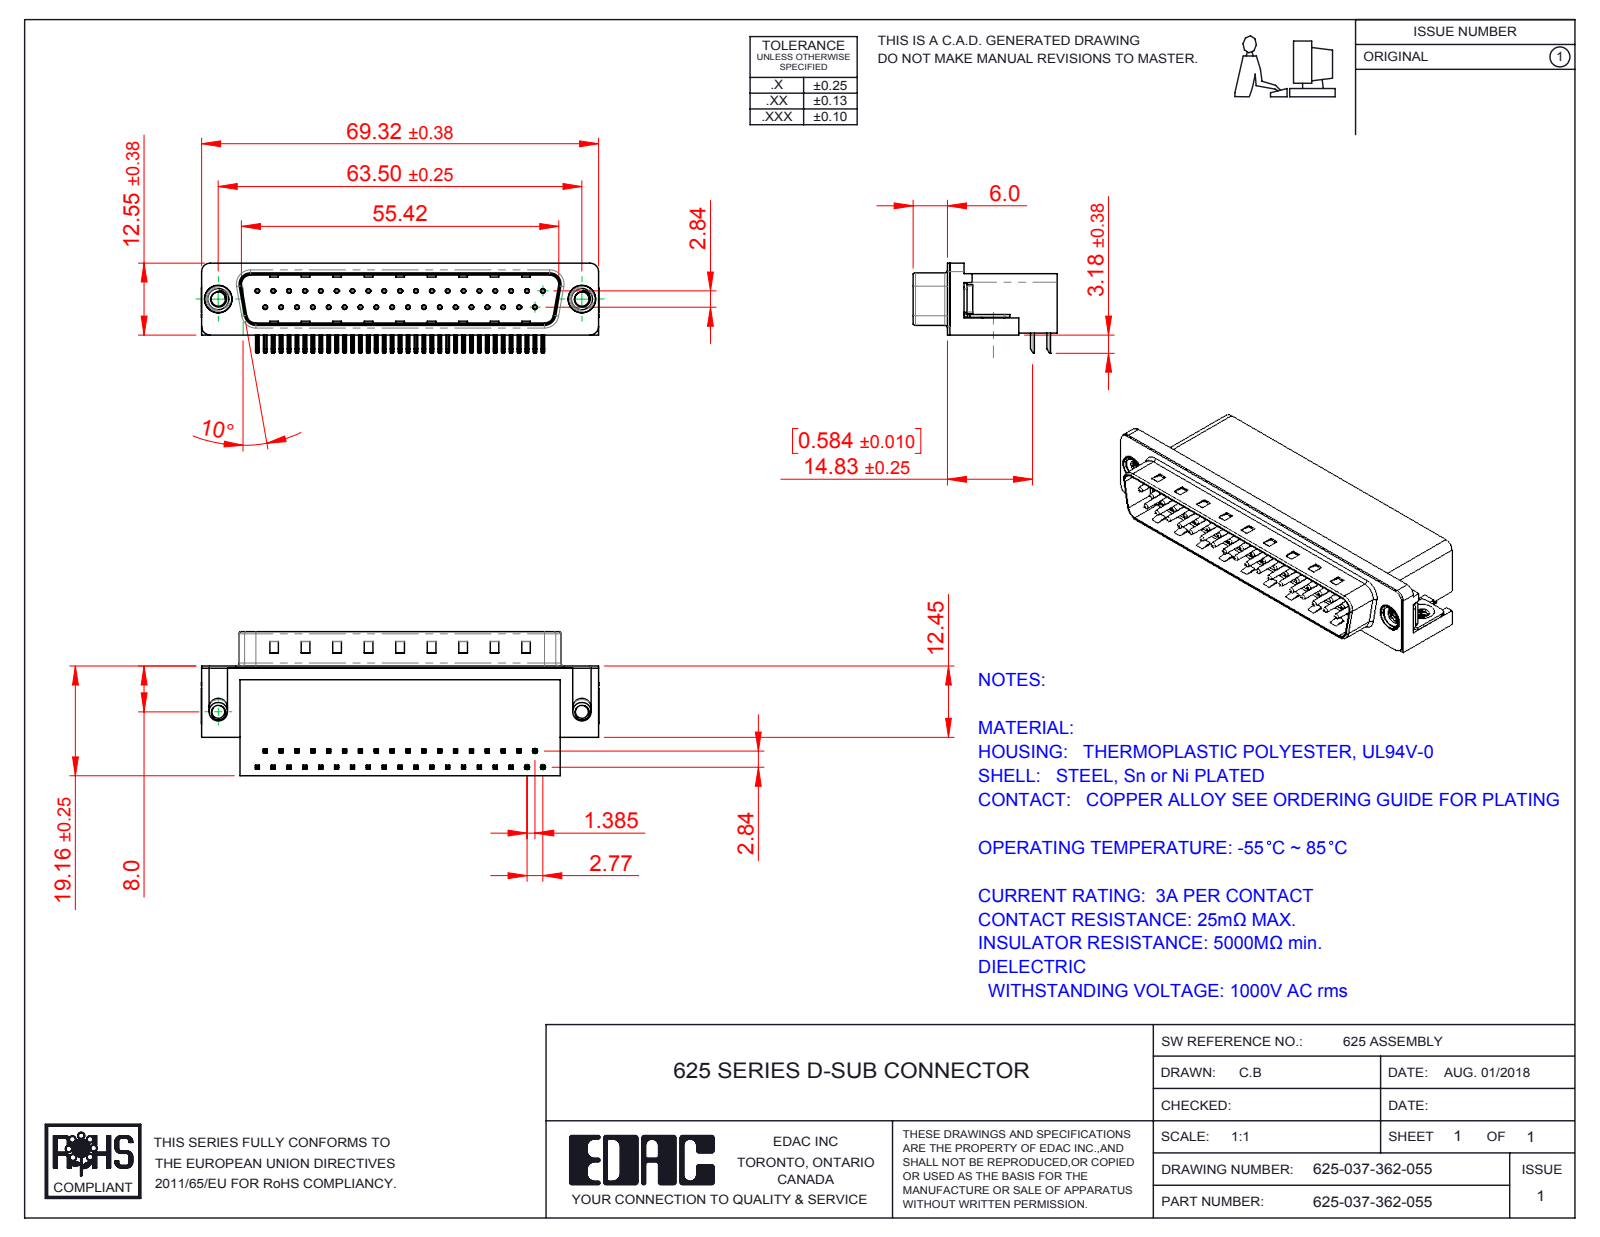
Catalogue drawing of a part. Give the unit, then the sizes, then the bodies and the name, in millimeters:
Units: millimetres
Overall size (bounding box): 69.4 × 25.16 × 15.73
Round holes (diameter × count): ⌀0.35 ×37, ⌀0.8 ×37, ⌀2.26 ×2, ⌀2.5 ×2, ⌀4 ×2, ⌀4.8 ×2, ⌀5 ×2
Round bosses / shafts (diameter × count): ⌀0.75 ×37, ⌀4.9 ×2, ⌀4.75 ×2, ⌀3.9 ×2, ⌀3.26 ×2
Partial cylindrical surfaces — rounded edges, fillets, slot ends (radius × count): R0.25 ×156, R0.12 ×74, R1 ×16, R0.5 ×9, R1.6 ×8, R1.5 ×7, R0.9 ×4, R2 ×4
Main face-to-face distances: 10.34, 0.4, 18.76, 8.76, 19.16, 2.84, 2.09, 10.1, 1.74, 8.36
Hole centre spacings: 3.16, 2.77, 5.54, 8.31, 11.08, 13.85, 19.39, 22.16
Volume: 12 606 mm³ · Surface area: 11 837 mm²
Bodies: 43 solids, 3233 faces (2015 planar, 933 cylindrical, 285 other)
Part name (STEP PRODUCT): 625 M3 Threaded Rivet; 625 4-40 Threaded Board Mount; 625 Contact Top; 625 Contact Bottom (+3 more)
STEP written by: SolidWorks 2016 (CONFIG_CONTROL_DESIGN)
